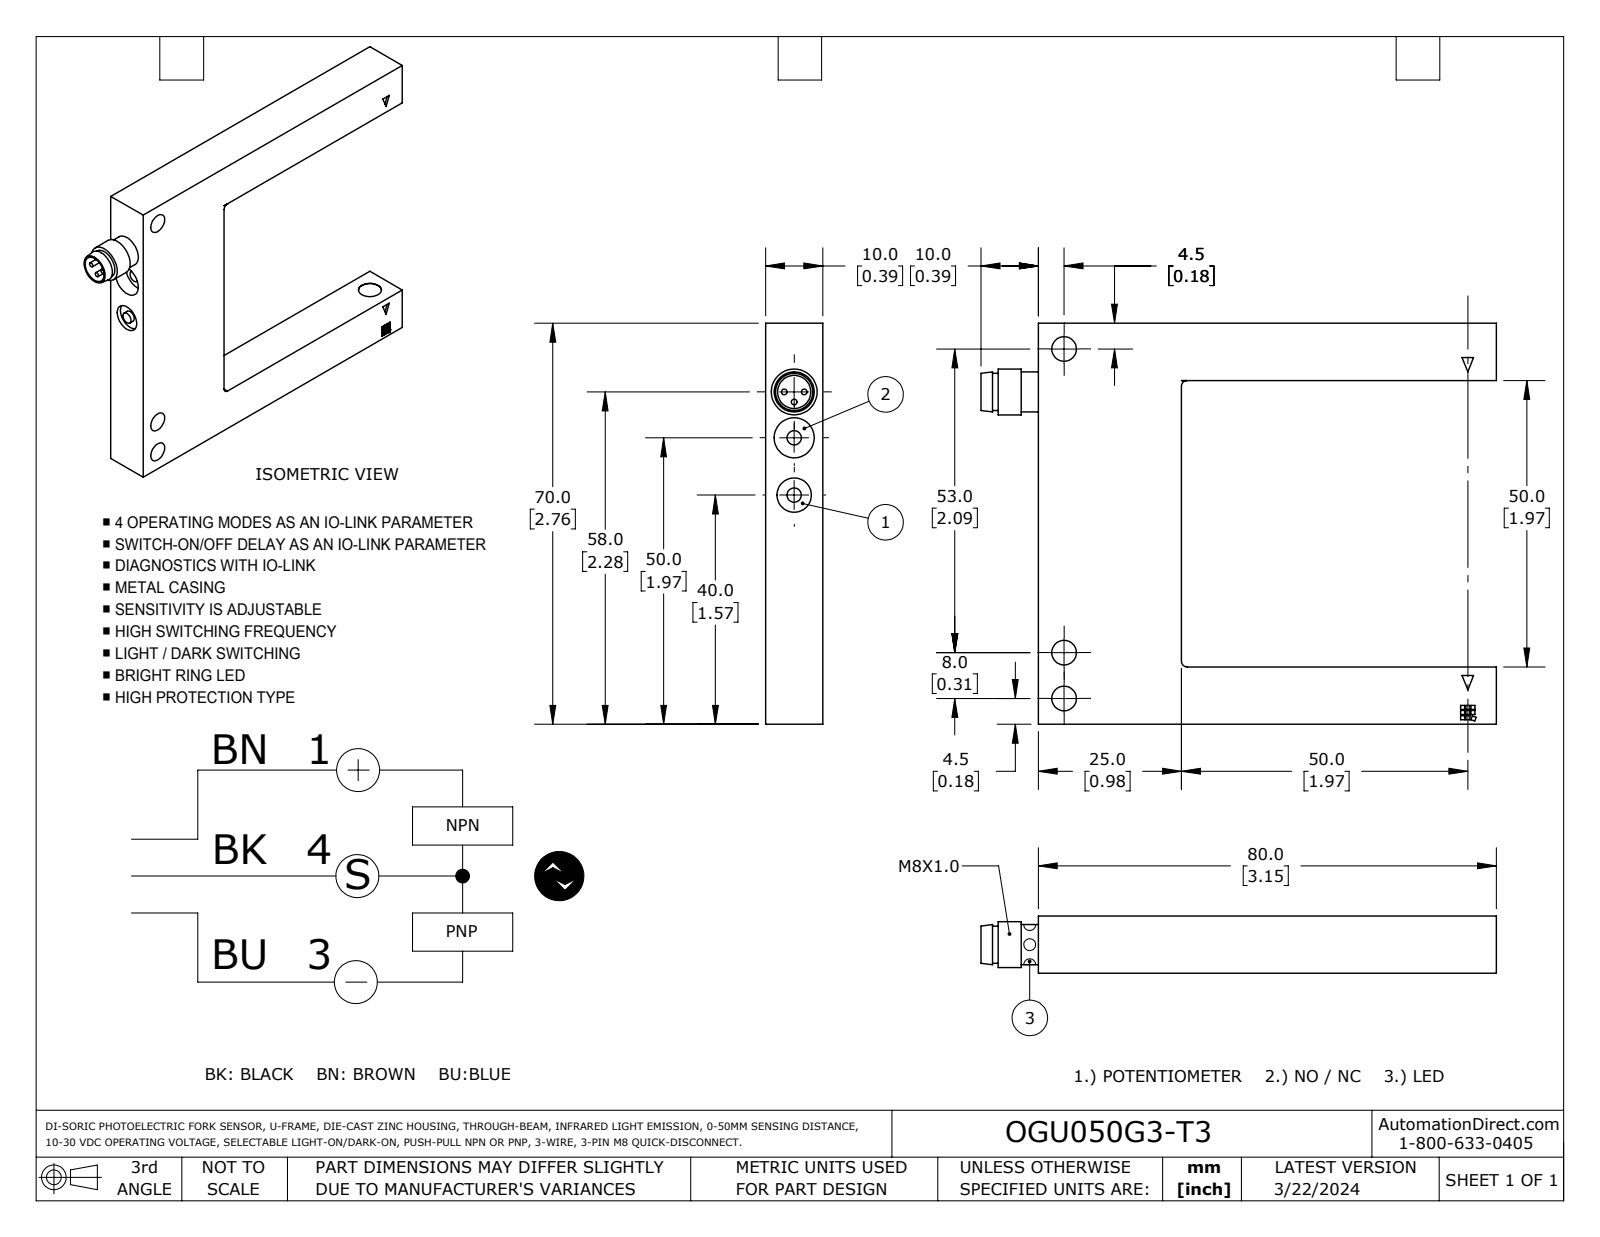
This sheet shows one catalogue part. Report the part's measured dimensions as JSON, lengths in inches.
{"part_name": "OGU050G3-T3", "step_written_by": "SolidWorks 2023 (AUTOMOTIVE_DESIGN)", "units": "inches", "bodies": {"solids": 1, "faces": 112, "planar": 91, "cylindrical": 20, "other": 1}, "overall_size": [3.543, 2.756, 0.394], "volume_in3": 1.722, "surface_area_in2": 16.5, "round_holes": [[0.169, 3], [0.118, 1], [0.197, 1], [0.228, 1], [0.236, 1], [0.276, 1]], "round_bosses_or_shafts": [[0.039, 3], [0.098, 2], [0.315, 1], [0.276, 1], [0.256, 1]], "partial_cylinders_radius": [[0.039, 3]], "face_to_face_distances": [0.394, 2.362, 2.756, 1.969, 0.984, 3.15, 2.165, 0.392, 0.039, 2.364], "hole_center_spacings": [0.315, 0.394, 0.709, 2.087, 2.402]}
